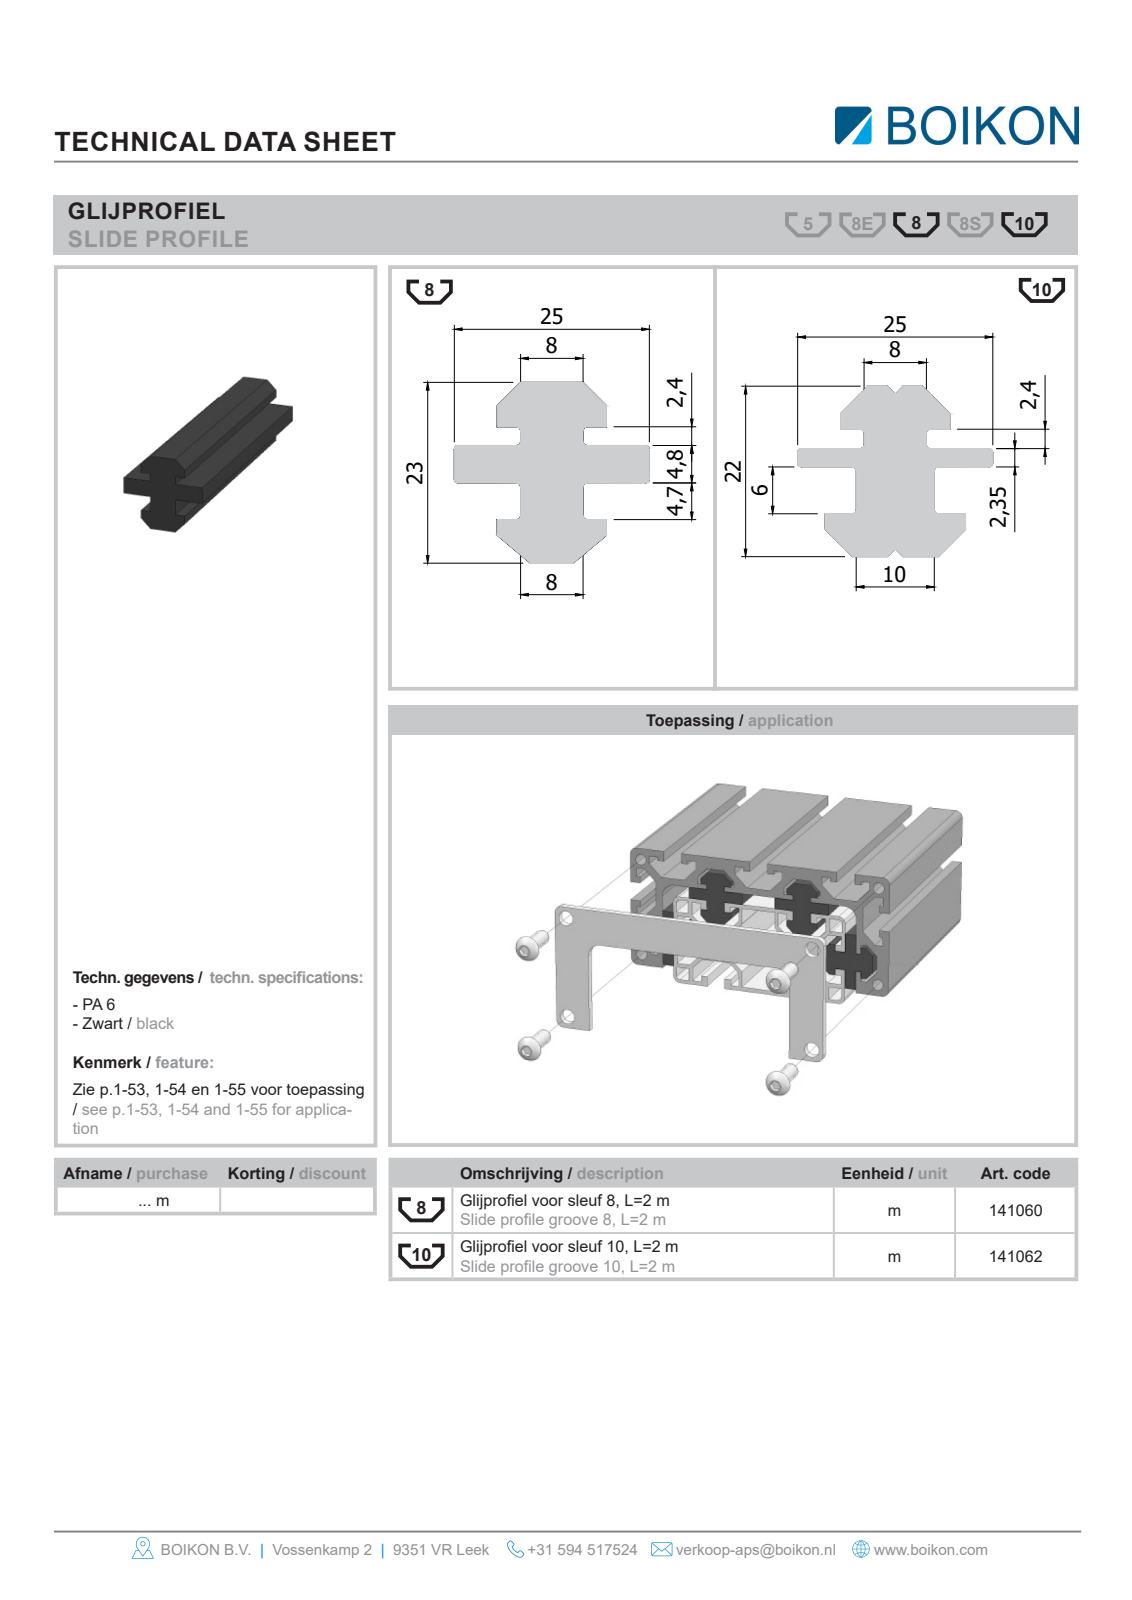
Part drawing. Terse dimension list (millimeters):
name: Root; 141062Glijprofiel sleuf 10-8eBOIKON0
written by: HiCAD 2013 1802.4 Build 509 (AUTOMOTIVE_DESIGN)
unit: mm
bodies: 1 solid, 26 faces (26 planar, 0 cylindrical, 0 other)
size: 1000 × 25 × 22.3
volume: 299 535 mm³; area: 114 798 mm²
face distances: 2.4, 8.45, 5.5, 12.05, 14.45, 2, 22.13, 6, 6.05, 22.3
